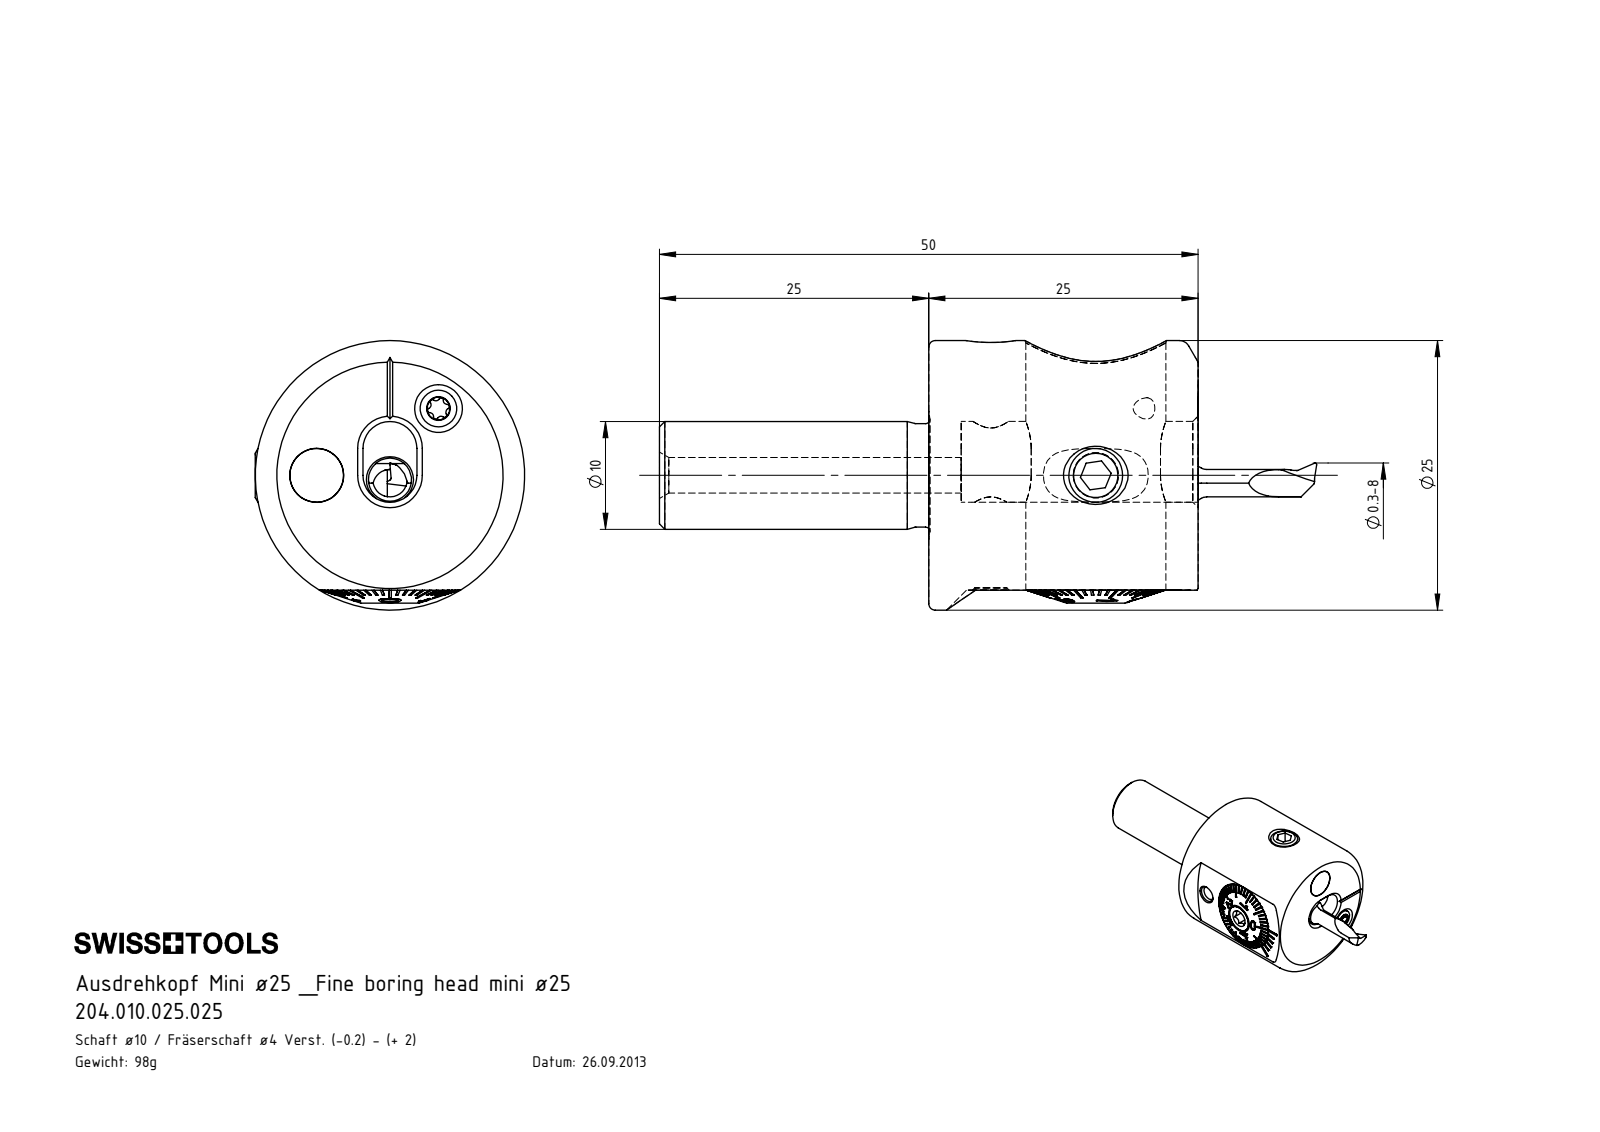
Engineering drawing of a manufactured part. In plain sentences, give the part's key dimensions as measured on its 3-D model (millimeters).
The part is named "A25-BG2.008.004_A; Mini_Schaft_4; F25-BG2.013.003_A; ISO 4026 - M4 x 8 (+8 more)". Its 3-D file was written by "SolidWorks 2017 (CONFIG_CONTROL_DESIGN)". It is 16 solids with 741 faces: 313 planar, 138 cylindrical and 290 other. Overall it measures 61 by 25 by 25 millimeters. Its volume is 12 767 cubic millimeters and its surface area 9 402 square millimeters. Round holes: 4 of diameter 3.3, 2 of diameter 2, 2 of diameter 4.2, 2 of diameter 5, 1 of diameter 1, 1 of diameter 2.4, 1 of diameter 2.7, 1 of diameter 3, 1 of diameter 4, 1 of diameter 6.75, 1 of diameter 7.3, 1 of diameter 7.4. Round bosses or shafts: 3 of diameter 4, 2 of diameter 4.95, 1 of diameter 25, 1 of diameter 13, 1 of diameter 12.98, 1 of diameter 12.85, 1 of diameter 10.65, 1 of diameter 10. Partial cylindrical surfaces (rounded edges, fillets, slot ends): 6 of radius 0.21, 5 of radius 0.36, 4 of radius 0.2, 4 of radius 2.2, 2 of radius 1.6, 2 of radius 2.5, 1 of radius 0.36, 1 of radius 0.5. The main face-to-face distances are 25, 3.9, 1.5, 0.8, 3.1, 3.8, 1.6, 2.3, 8, 3. The hole center spacings are 3.5, 7.66, 0.4, 6.25, 6.8, 6.81, 7, 7.99.
